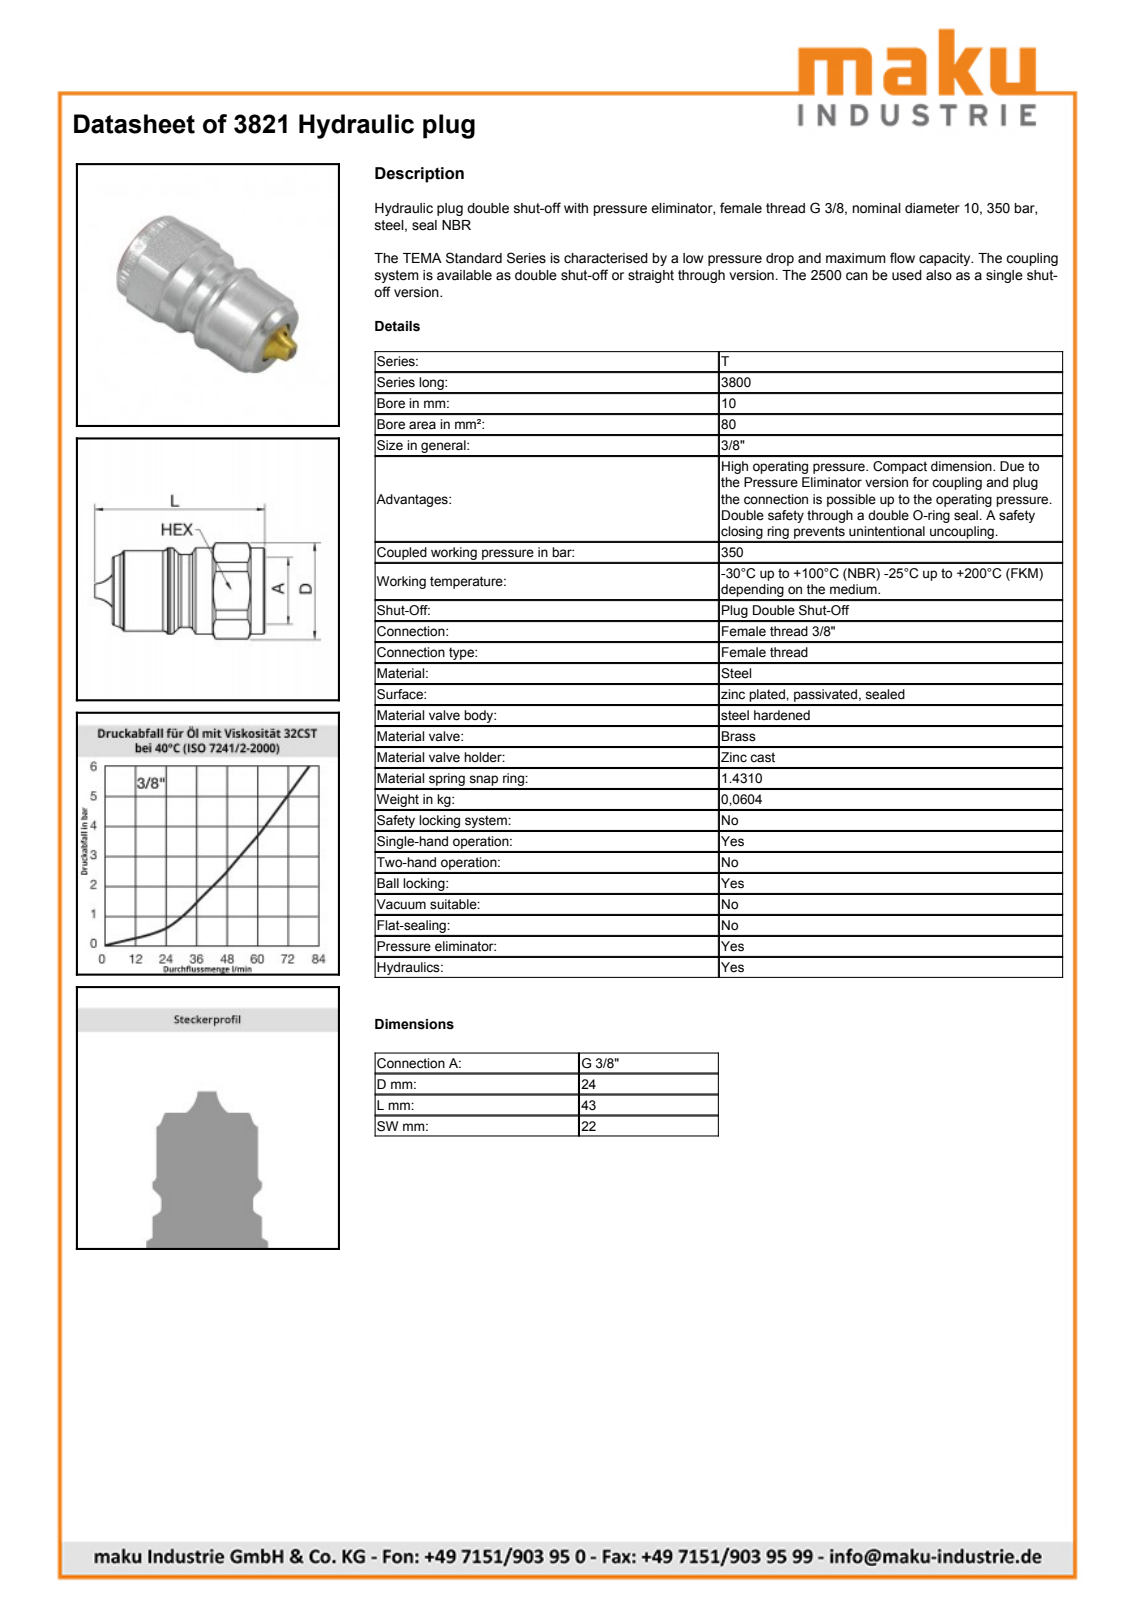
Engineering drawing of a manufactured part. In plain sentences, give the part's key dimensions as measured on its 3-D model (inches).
The part is named "3821". Its 3-D file was written by "SolidWorks 2009 (AUTOMOTIVE_DESIGN)". It is 1 solid with 71 faces: 13 planar, 22 cylindrical and 36 other. Overall it measures 1.685 by 0.945 by 0.866 inches. Its volume is 0.635 cubic inches and its surface area 6.25 square inches. Round holes: 1 of diameter 0.155, 1 of diameter 0.394, 1 of diameter 0.589. Round bosses or shafts: 1 of diameter 0.846, 1 of diameter 0.844, 1 of diameter 0.778, 1 of diameter 0.72. Partial cylindrical surfaces (rounded edges, fillets, slot ends): 1 of radius 0.472. The main face-to-face distances are 0.866, 0.915, 1.496, 0.581, 0.172, 1.087, 1.668, 0.174, 1.089, 1.67.
